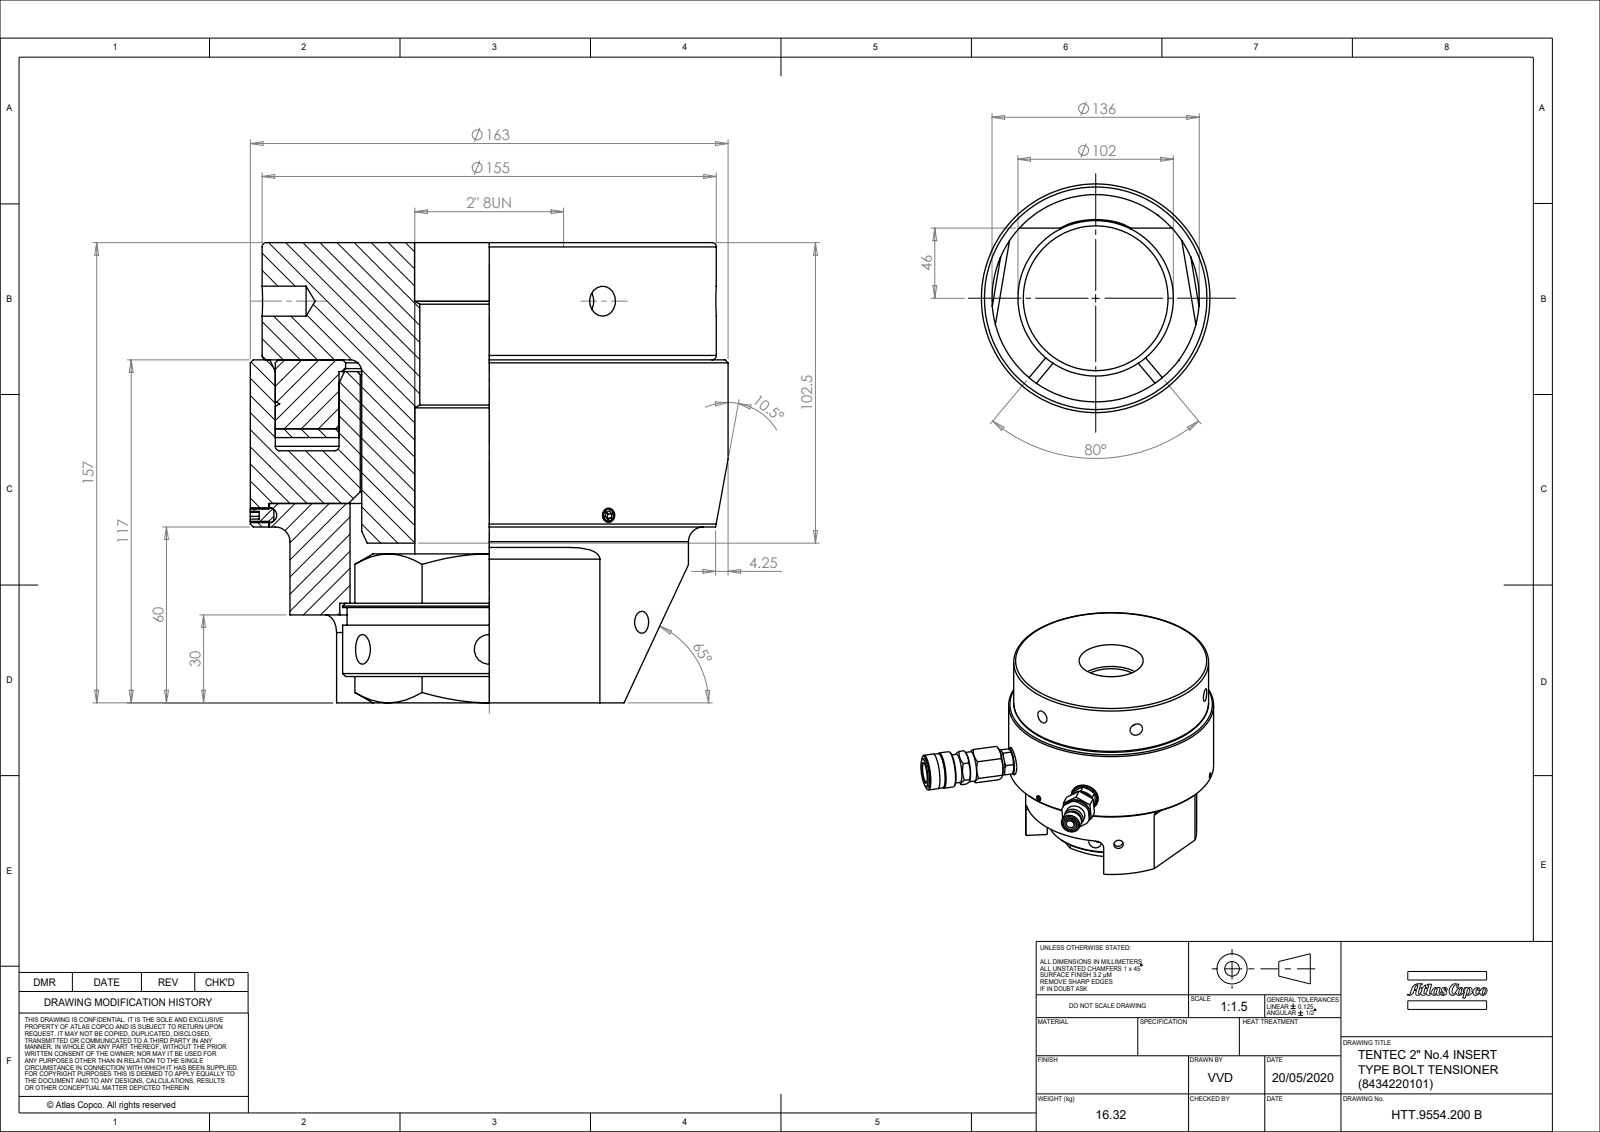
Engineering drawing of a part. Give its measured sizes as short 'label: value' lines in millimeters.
name: CTST_04-2_INCH_8434220101
written by: CREO PARAMETRIC BY PTC INC, 2020281 (CONFIG_CONTROL_DESIGN)
unit: mm
bodies: 1 solid, 432 faces (136 planar, 146 cylindrical, 150 other)
size: 220.47 × 169.67 × 157
volume: 2 660 000 mm³; area: 166 860 mm²
holes: 4× ⌀7.5, 3× ⌀2.5, 3× ⌀10.2, 2× ⌀3, 2× ⌀9, 2× ⌀11.6, 2× ⌀11.8, 2× ⌀13.74, 2× ⌀22, 1× ⌀15, 1× ⌀15.63, 1× ⌀50.92
bosses: 3× ⌀11, 3× ⌀5, 2× ⌀20.57, 1× ⌀163, 1× ⌀155, 1× ⌀150, 1× ⌀146, 1× ⌀136
rounds: 2× R4, 2× R6, 1× R11.6, 1× R28.04
face distances: 157, 117, 40, 60, 57, 97, 30, 9, 51, 108
